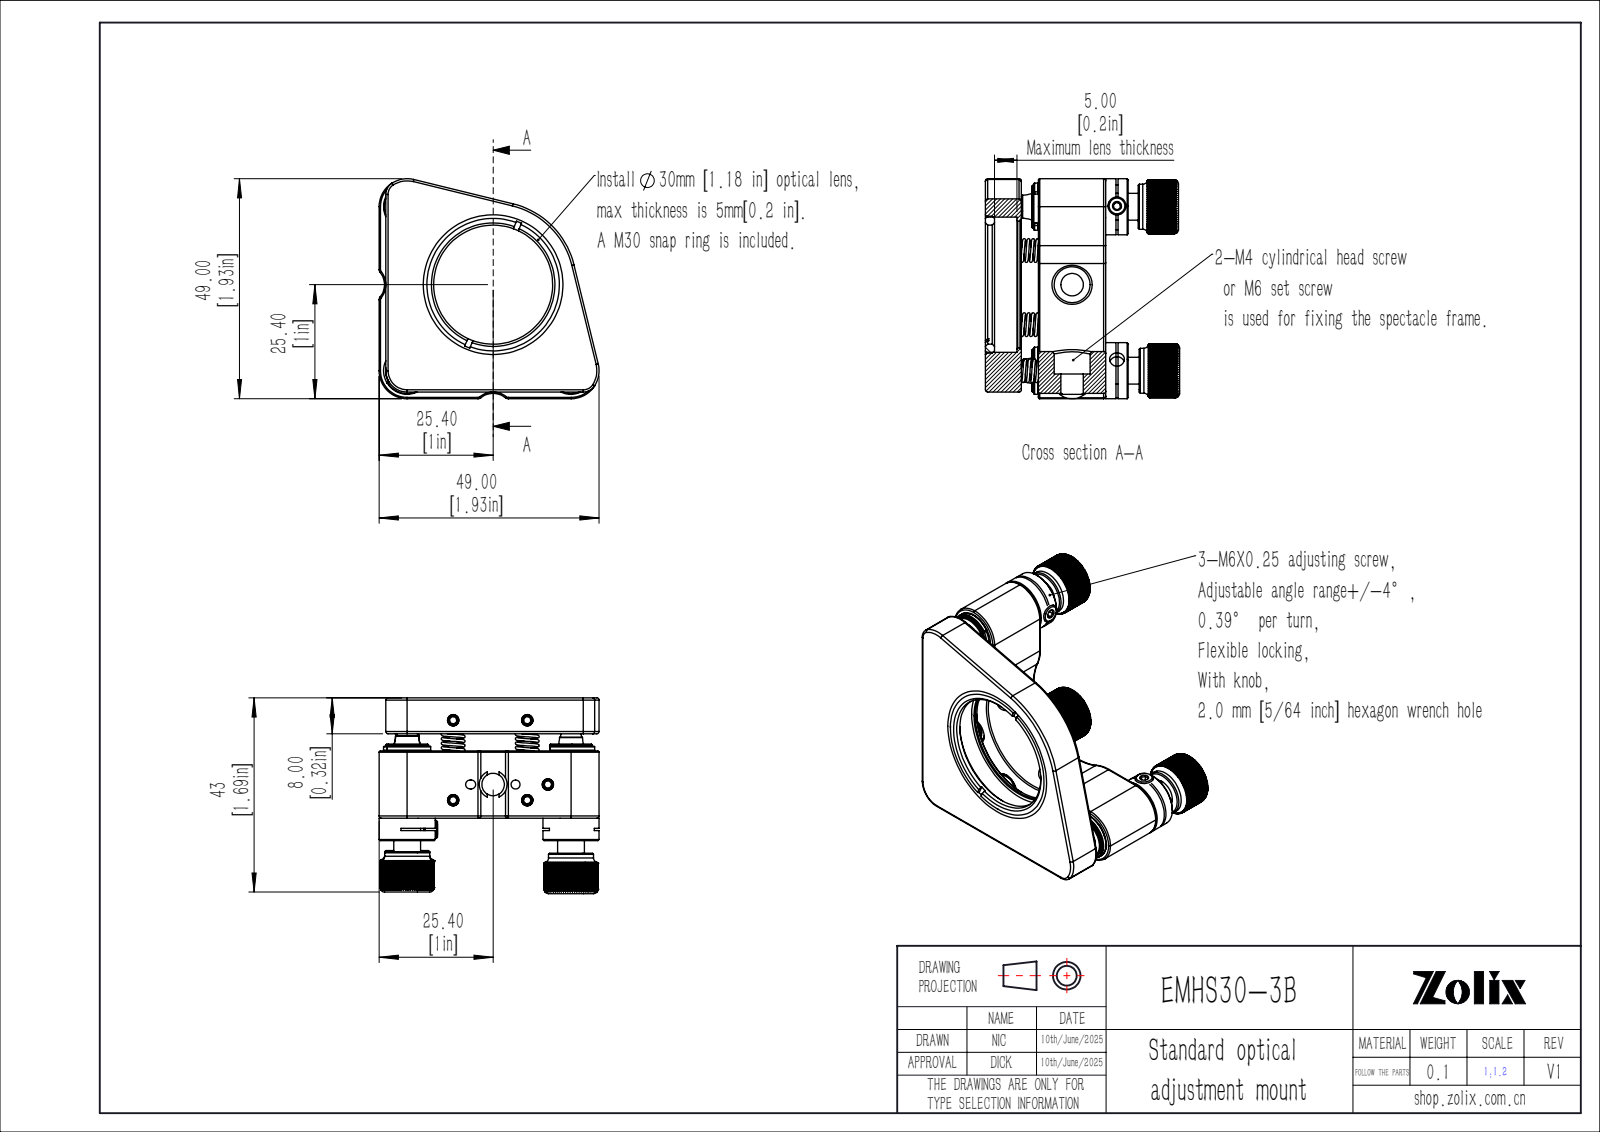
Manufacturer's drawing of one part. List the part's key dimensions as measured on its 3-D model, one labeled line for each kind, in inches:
Part name (STEP PRODUCT): EMHS30-3B
STEP written by: SolidWorks 2020 (CONFIG_CONTROL_DESIGN)
Units: inches
Bodies: 0 solids, 1280 faces (608 planar, 397 cylindrical, 275 other)
Overall size (bounding box): 1.929 × 1.929 × 1.717
Round holes (diameter × count): ⌀0.236 ×6, ⌀0.118 ×4, ⌀0.157 ×2, ⌀0.13 ×1, ⌀0.181 ×1, ⌀0.248 ×1, ⌀0.394 ×1, ⌀0.413 ×1, ⌀1.043 ×1, ⌀1.11 ×1, ⌀1.185 ×1
Round bosses / shafts (diameter × count): ⌀0.315 ×5, ⌀0.118 ×4, ⌀0.492 ×3, ⌀0.374 ×3, ⌀0.157 ×3, ⌀0.394 ×2, ⌀0.197 ×2, ⌀0.079 ×2
Partial cylindrical surfaces — rounded edges, fillets, slot ends (radius × count): R0.02 ×12, R0.039 ×8, R0.012 ×7, R0.031 ×4, R0.236 ×3, R0.118 ×2, R0.122 ×2, R0.171 ×2
Main face-to-face distances: 0.315, 0.059, 1.055, 0.74, 0.15, 0.465, 0.591, 0.089, 0.108, 0.197
Hole centre spacings: 0.65, 0.384, 0.404, 0.811, 0.831, 1.017, 1.033, 1.053
